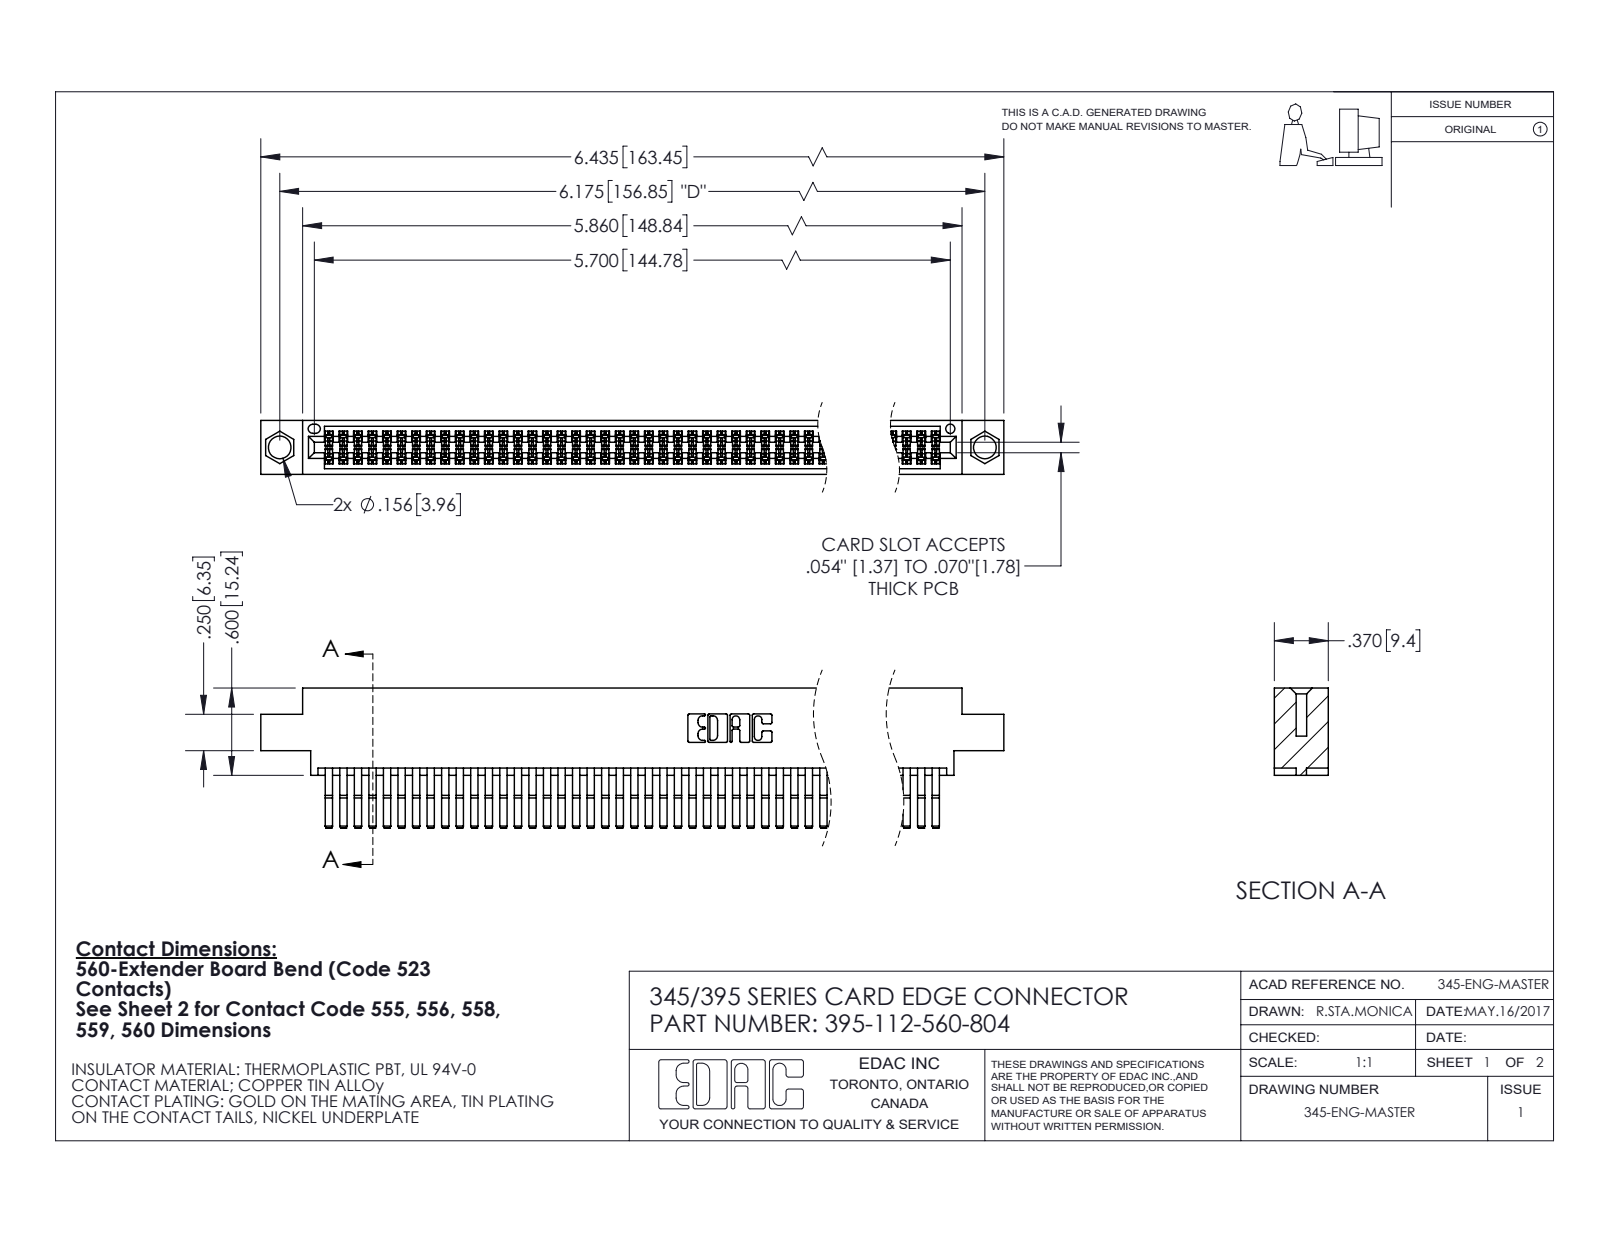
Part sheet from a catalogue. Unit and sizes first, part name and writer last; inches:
Units: inches
Overall size (bounding box): 6.435 × 0.962 × 0.37
Round holes (diameter × count): ⌀0.156 ×2, ⌀0.064 ×1
Partial cylindrical surfaces — rounded edges, fillets, slot ends (radius × count): R0.006 ×168, R0.01 ×22, R0.007 ×6, R0.031 ×6, R0.026 ×3, R0.01 ×2, R0.014 ×2, R0.019 ×2
Main face-to-face distances: 0.025, 0.298, 0.072, 0.37, 0.2, 0.098, 0.272, 0.225, 0.175, 0.149
Hole centre spacings: 0.27, 5.939, 6.175
Volume: 1.008 in³ · Surface area: 41.19 in²
Bodies: 113 solids, 5968 faces (3794 planar, 2174 cylindrical, 0 other)
Part name (STEP PRODUCT): 345 Part_0.170 Offset - 0.156 Dia-TI; 345-292-001_560 Tail; 395-112-560-804
STEP written by: SolidWorks 2020 (CONFIG_CONTROL_DESIGN)
